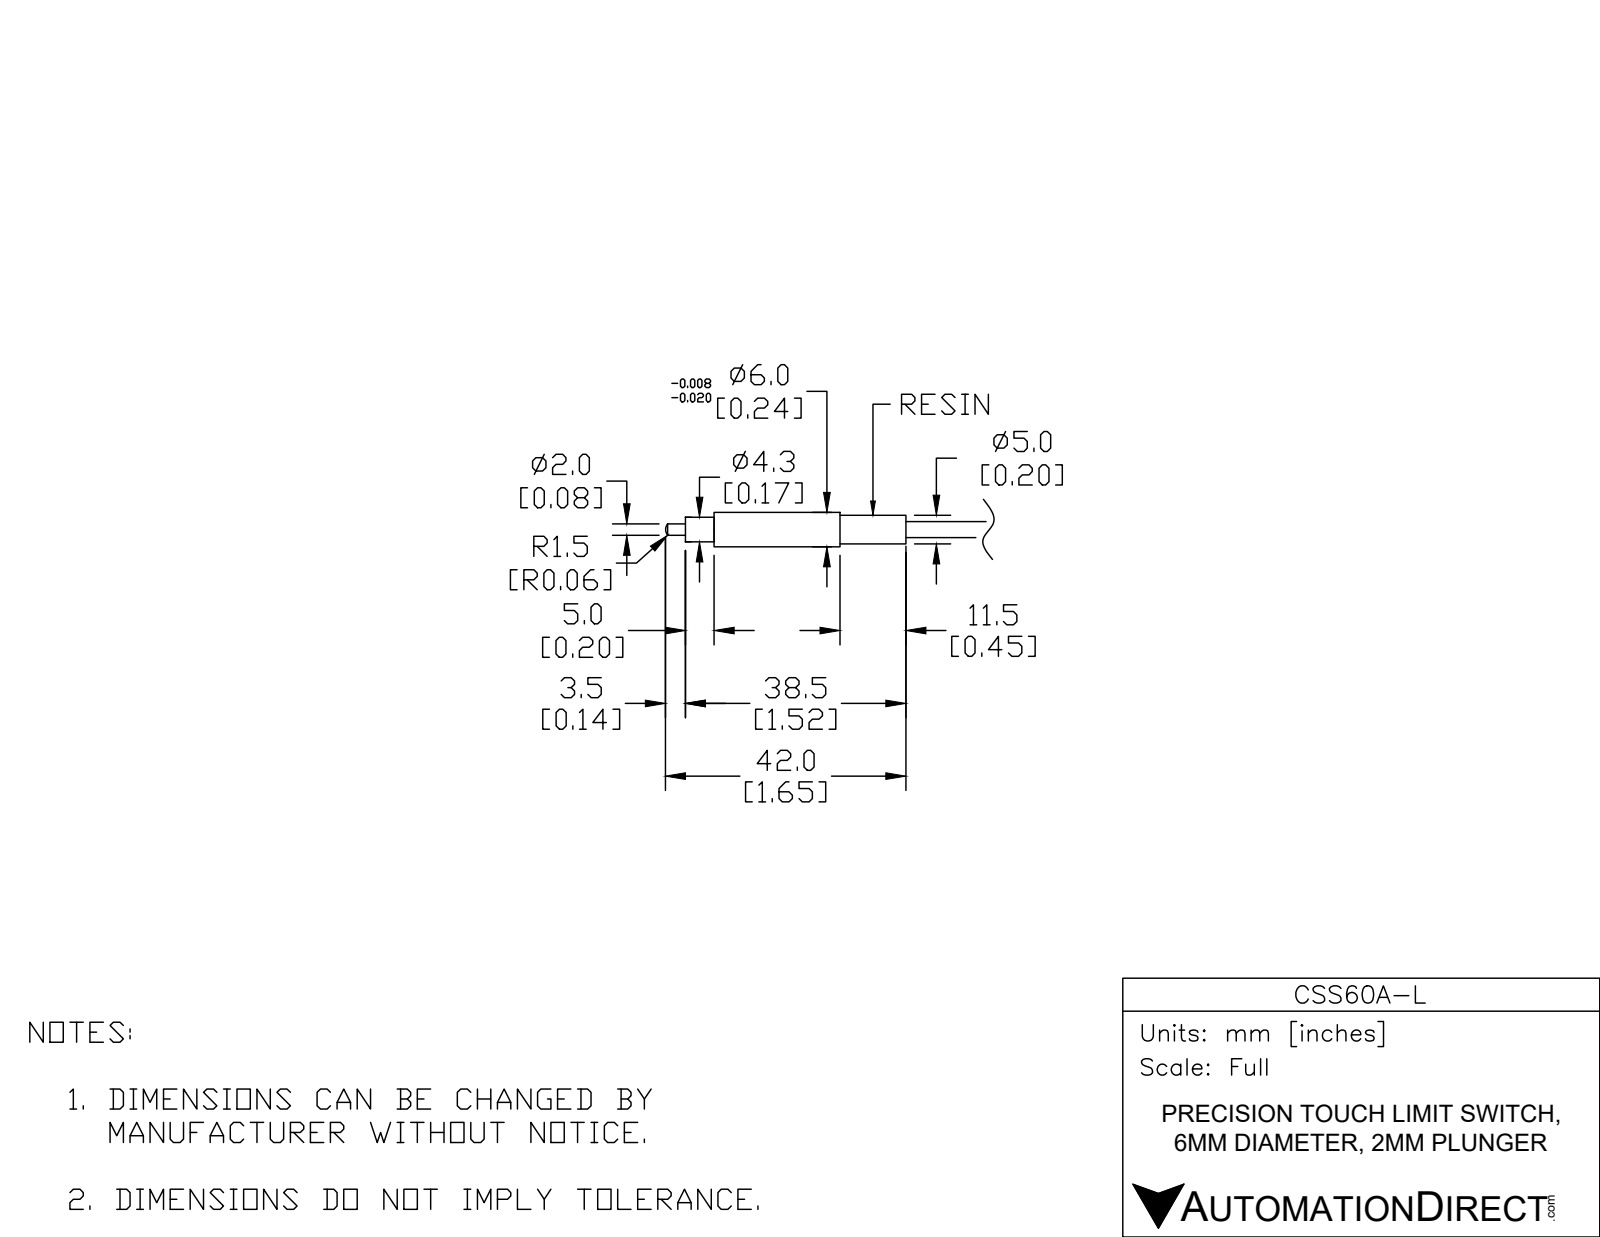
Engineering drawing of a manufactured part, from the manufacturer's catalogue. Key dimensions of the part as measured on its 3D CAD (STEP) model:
STEP written by: Spatial InterOp 3D (CONFIG_CONTROL_DESIGN)
Units: millimetres
Bodies: 1 solid, 17 faces (5 planar, 10 cylindrical, 2 other)
Overall size (bounding box): 56 × 6 × 6
Volume: 1 017 mm³ · Surface area: 863 mm²
Round bosses / shafts (diameter × count): ⌀6 ×1, ⌀5 ×1, ⌀4.3 ×1, ⌀2.8 ×1, ⌀2 ×1
Main face-to-face distances: 33.5, 5, 38.5, 27, 22, 11.5, 52.5, 47.5, 25.5, 14
